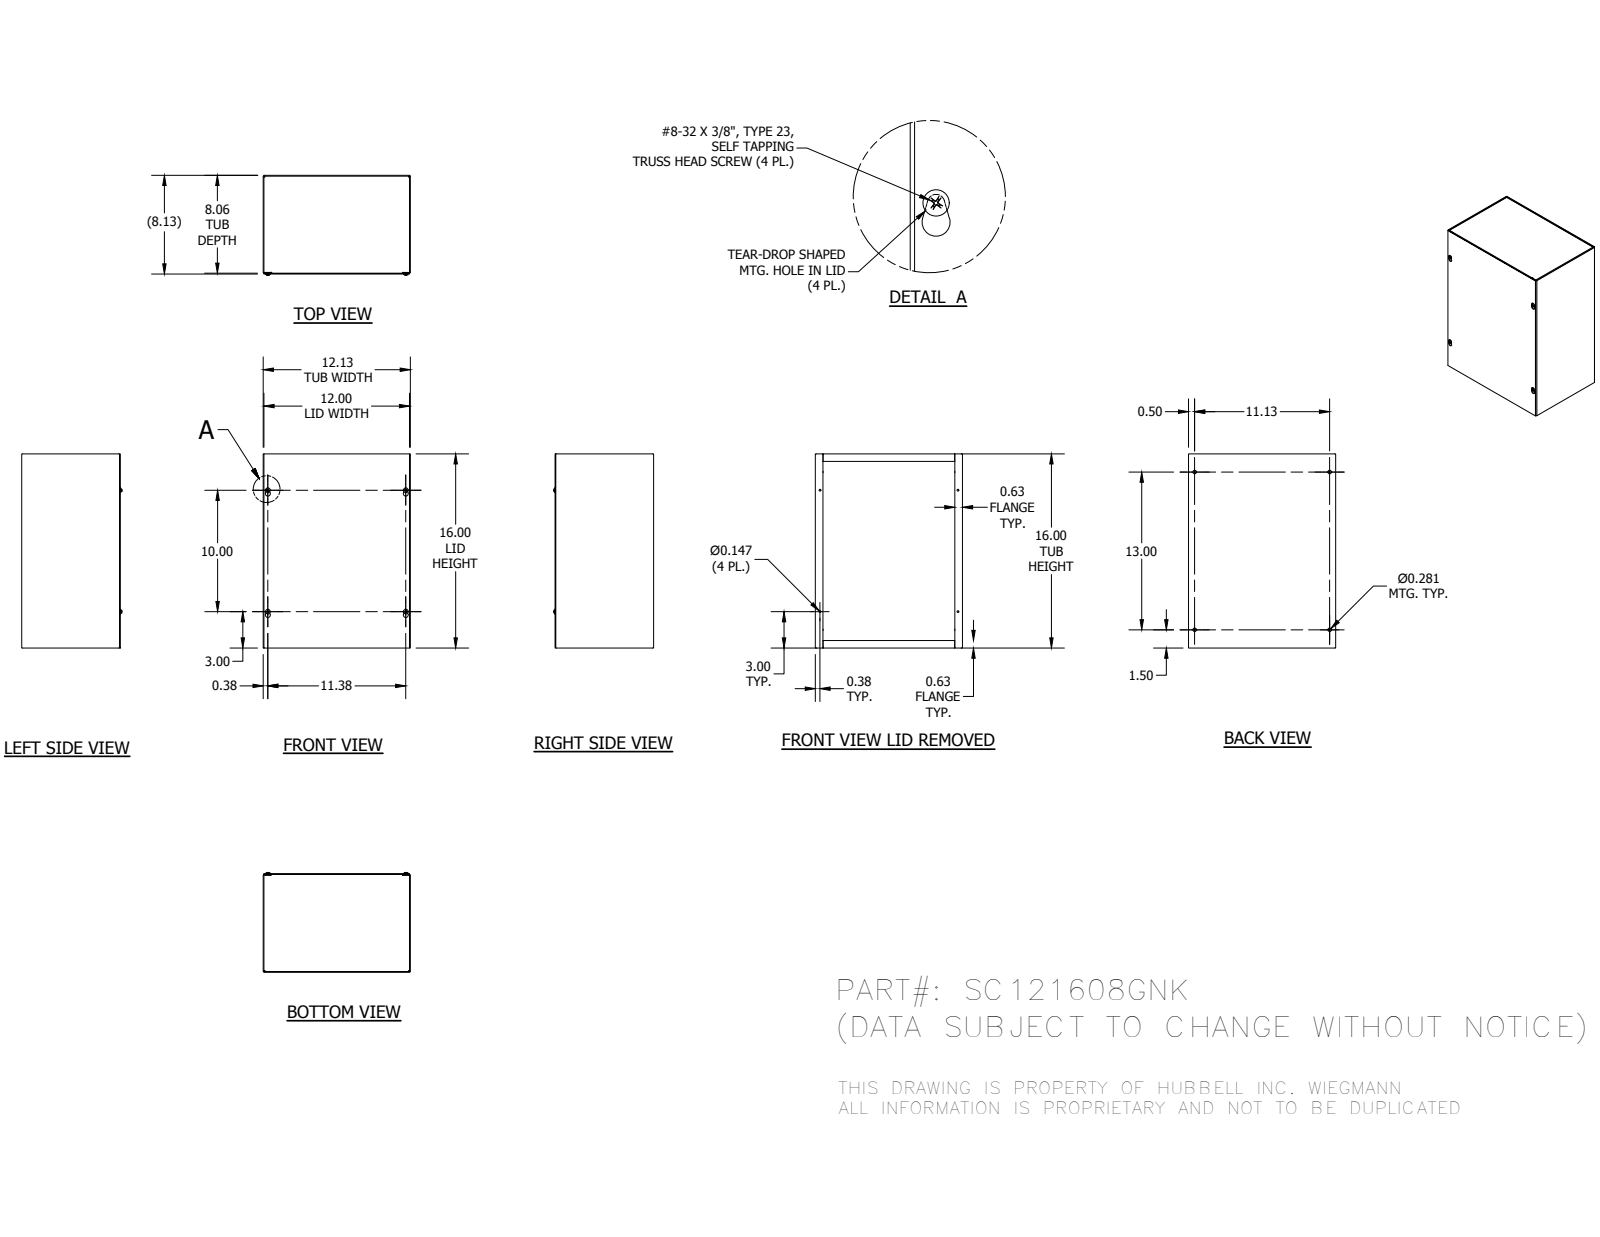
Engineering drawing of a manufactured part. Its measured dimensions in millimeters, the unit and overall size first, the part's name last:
Units: millimetres
Overall size (bounding box): 406.4 × 307.98 × 208.92
Round holes (diameter × count): ⌀3.73 ×4, ⌀7.14 ×4
Round bosses / shafts (diameter × count): ⌀9.75 ×4, ⌀4.17 ×4
Partial cylindrical surfaces — rounded edges, fillets, slot ends (radius × count): R0.4 ×12, R1.98 ×12, R3.17 ×4, R5.16 ×4
Main face-to-face distances: 1.59, 306.39, 203.2, 1.58, 204.78, 204.79, 206.37, 404.81, 304.8, 307.98
Hole centre spacings: 38.23, 288.28, 292.12, 408.63, 254, 282.58, 288.92, 330.2
Volume: 913 581 mm³ · Surface area: 1 161 000 mm²
Bodies: 8 solids, 268 faces (152 planar, 48 cylindrical, 68 other)
Part name (STEP PRODUCT): SC121608GNKBLR; SC1208GNKTB; SC1216GLPA; 34056 (+1 more)
STEP written by: Autodesk Inventor 2014 (AUTOMOTIVE_DESIGN)
